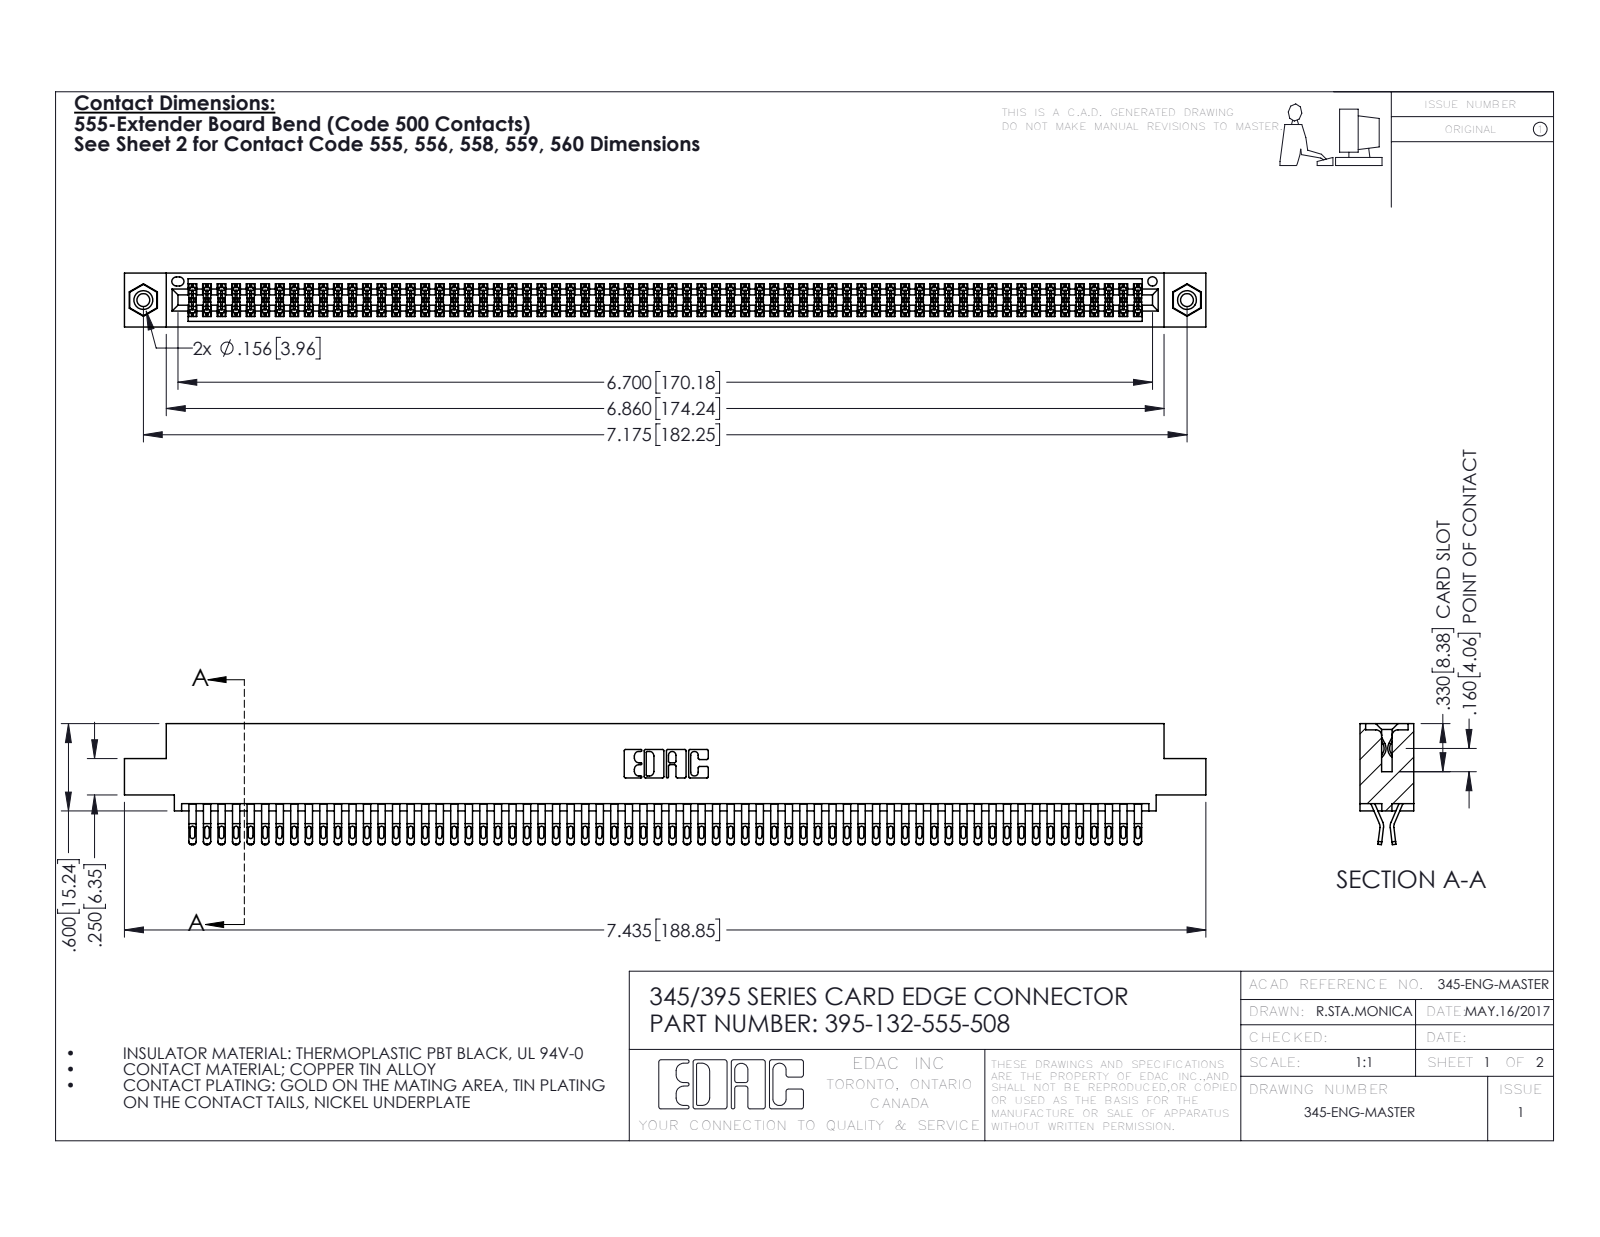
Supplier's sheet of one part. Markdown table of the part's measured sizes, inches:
| quantity | value |
| --- | --- |
| part name | 395-132-555-508; 345-292-001_555 Tail; 345-250-001_345-250-003-102; 345 Part_0.110 Offset - 0.156 Dia-TI |
| STEP written by | SolidWorks 2016 (CONFIG_CONTROL_DESIGN) |
| units | inches |
| bodies | 135 solids, 7582 faces (4208 planar, 3358 cylindrical, 16 other) |
| overall size | 7.435 × 0.832 × 0.37 |
| volume | 1.152 in³ |
| surface area | 46.19 in² |
| round holes (diameter × count) | 0.089 × 2, 0.125 × 2, 0.156 × 2, 0.064 × 1 |
| round bosses / shafts (diameter × count) | 0.155 × 2 |
| partial cylindrical surfaces (radius × count) | 0.016 × 330, 0.02 × 264, 0.006 × 198, 0.01 × 22, 0.007 × 6, 0.031 × 6, 0.026 × 3, 0.01 × 2 |
| main face-to-face distances | 0.072, 0.298, 0.025, 0.37, 0.2, 0.098, 0.272, 0.225, 0.175, 0.149 |
| hole center spacings | 0.27, 6.939, 7.175 |
